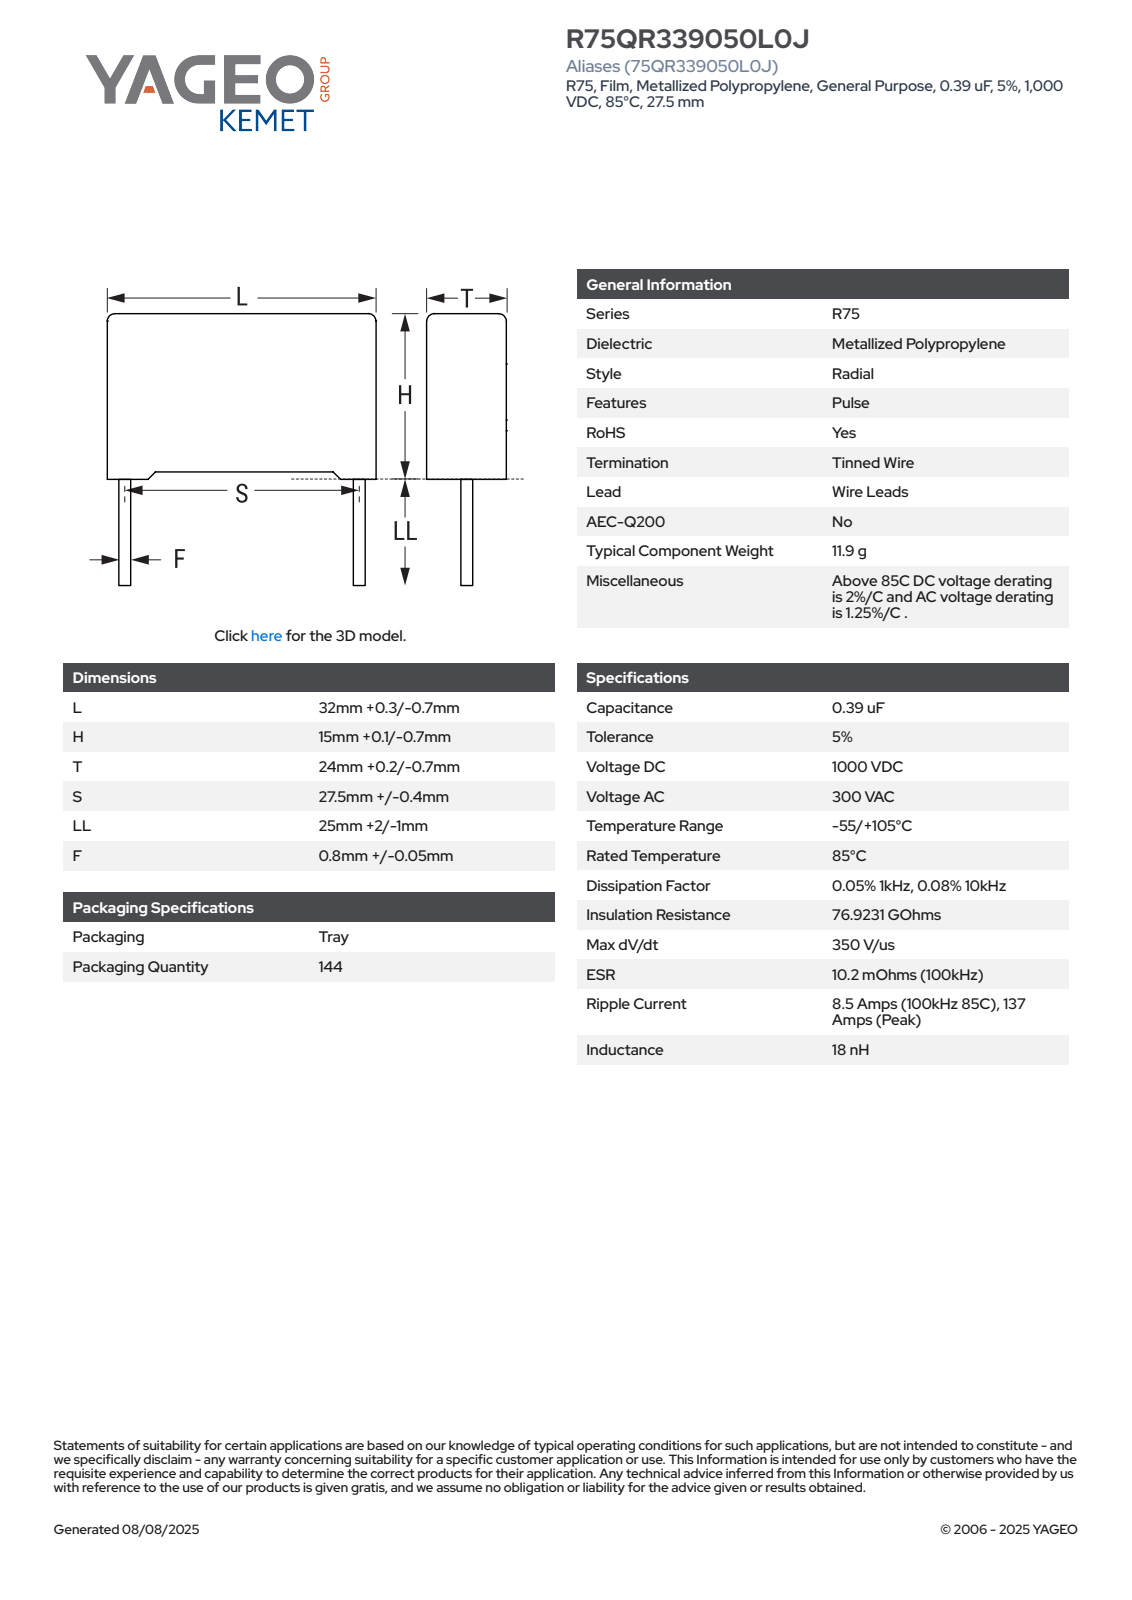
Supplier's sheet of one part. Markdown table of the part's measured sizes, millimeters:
| quantity | value |
| --- | --- |
| part name | CFR_RB2_32X15X24_L32.3H15.1T24.2S27.5LL27F0.85 |
| STEP written by | SolidWorks 2021 (AUTOMOTIVE_DESIGN) |
| units | millimeters |
| bodies | 4 solids, 85 faces (77 planar, 8 cylindrical, 0 other) |
| overall size | 42.1 × 32.3 × 24.2 |
| volume | 11 304 mm³ |
| surface area | 3 501 mm² |
| round bosses / shafts (diameter × count) | 0.85 × 2 |
| partial cylindrical surfaces (radius × count) | 0.5 × 4 |
| main face-to-face distances | 14.35, 24.2, 32.3, 0.75, 15.1, 1.08, 0.52, 14.58, 31.22, 23.12 |
